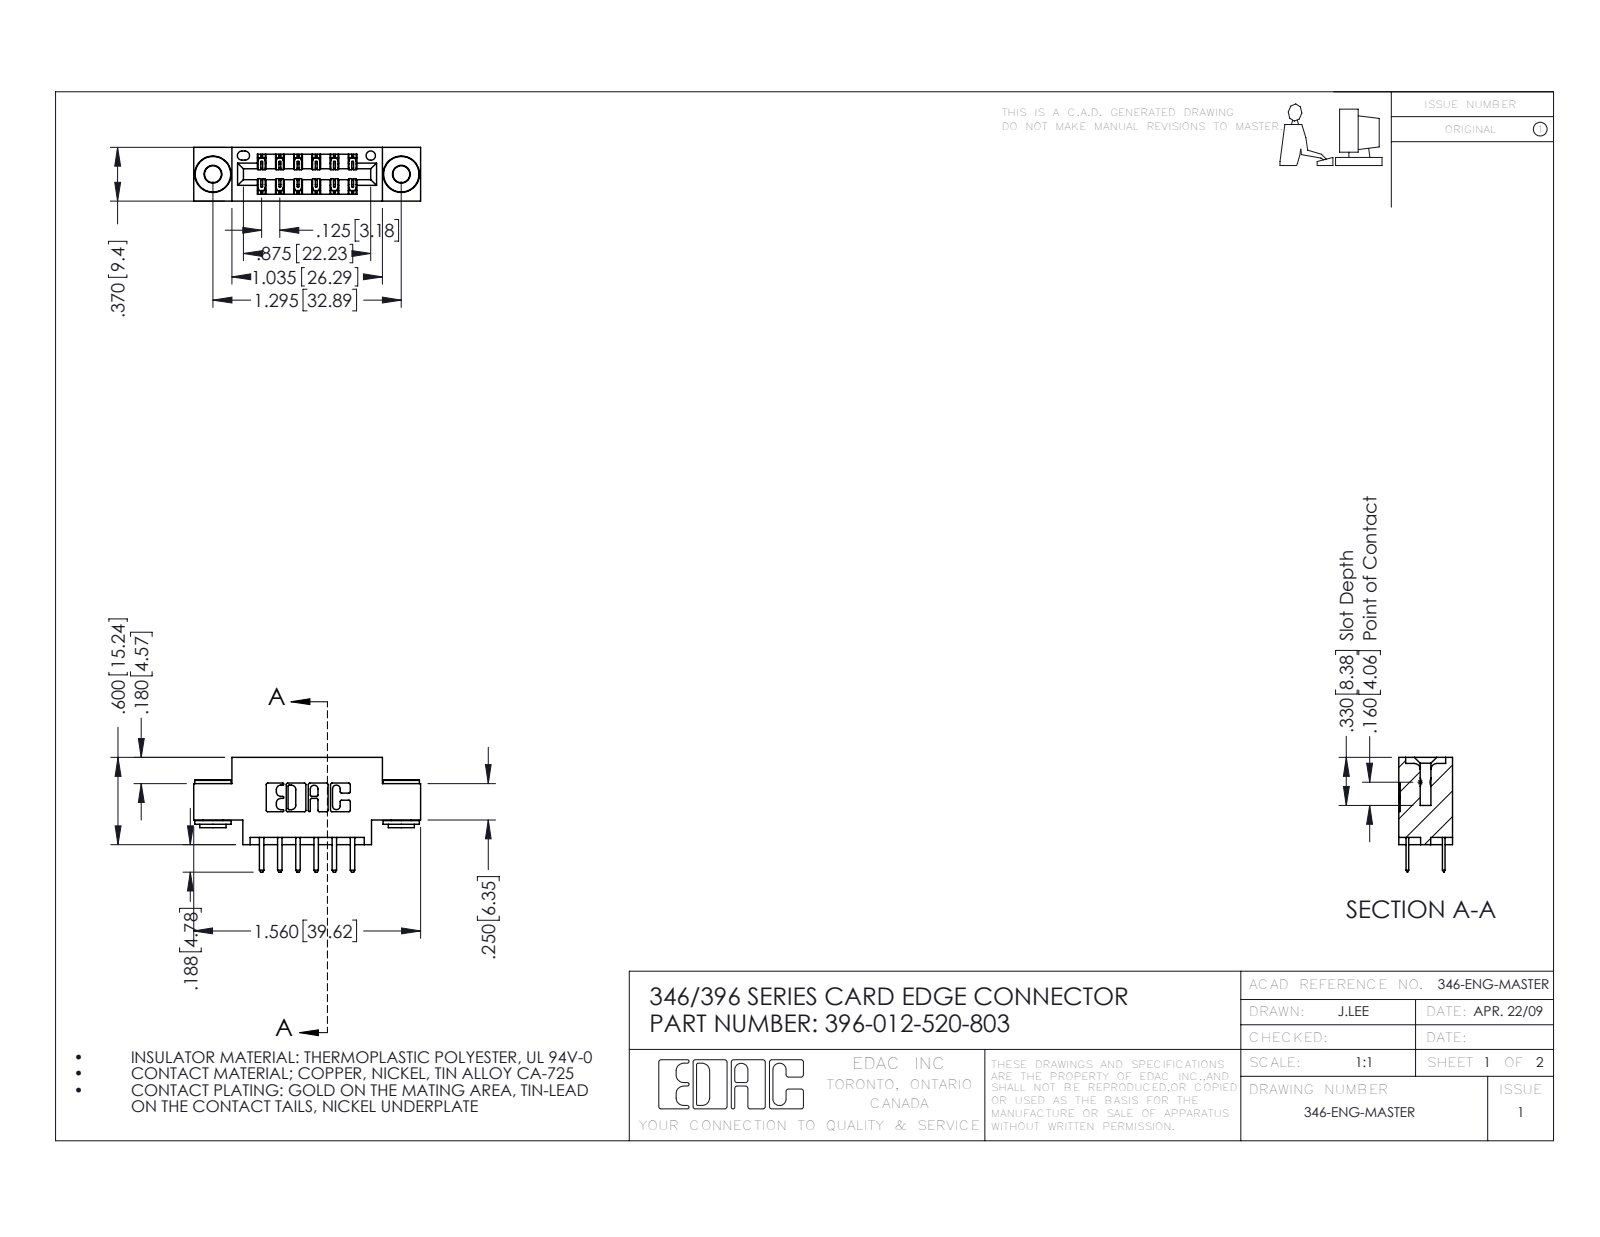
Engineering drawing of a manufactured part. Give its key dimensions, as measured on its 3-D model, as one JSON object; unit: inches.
{"part_name": "345-292-001_345-293-120; 396-012-520-803; 345-250-002_345-250-002-102; 346 Part_0.170 Offset - 0.156 Dia-TH", "step_written_by": "SolidWorks 2016 (CONFIG_CONTROL_DESIGN)", "units": "inches", "bodies": {"solids": 15, "faces": 836, "planar": 534, "cylindrical": 294, "other": 8}, "overall_size": [1.56, 0.788, 0.37], "volume_in3": 0.21, "surface_area_in2": 7.051, "round_holes": [[0.116, 2], [0.156, 2], [0.064, 1]], "round_bosses_or_shafts": [[0.25, 2], [0.18, 2], [0.136, 2]], "partial_cylinders_radius": [[0.01, 22], [0.006, 18], [0.01, 16], [0.007, 6], [0.031, 6], [0.026, 3], [0.014, 2], [0.022, 2]], "face_to_face_distances": [0.25, 0.37, 0.048, 0.322, 0.025, 0.275, 0.148, 0.222, 0.1, 0.174], "hole_center_spacings": [0.246, 1.092, 1.295]}
